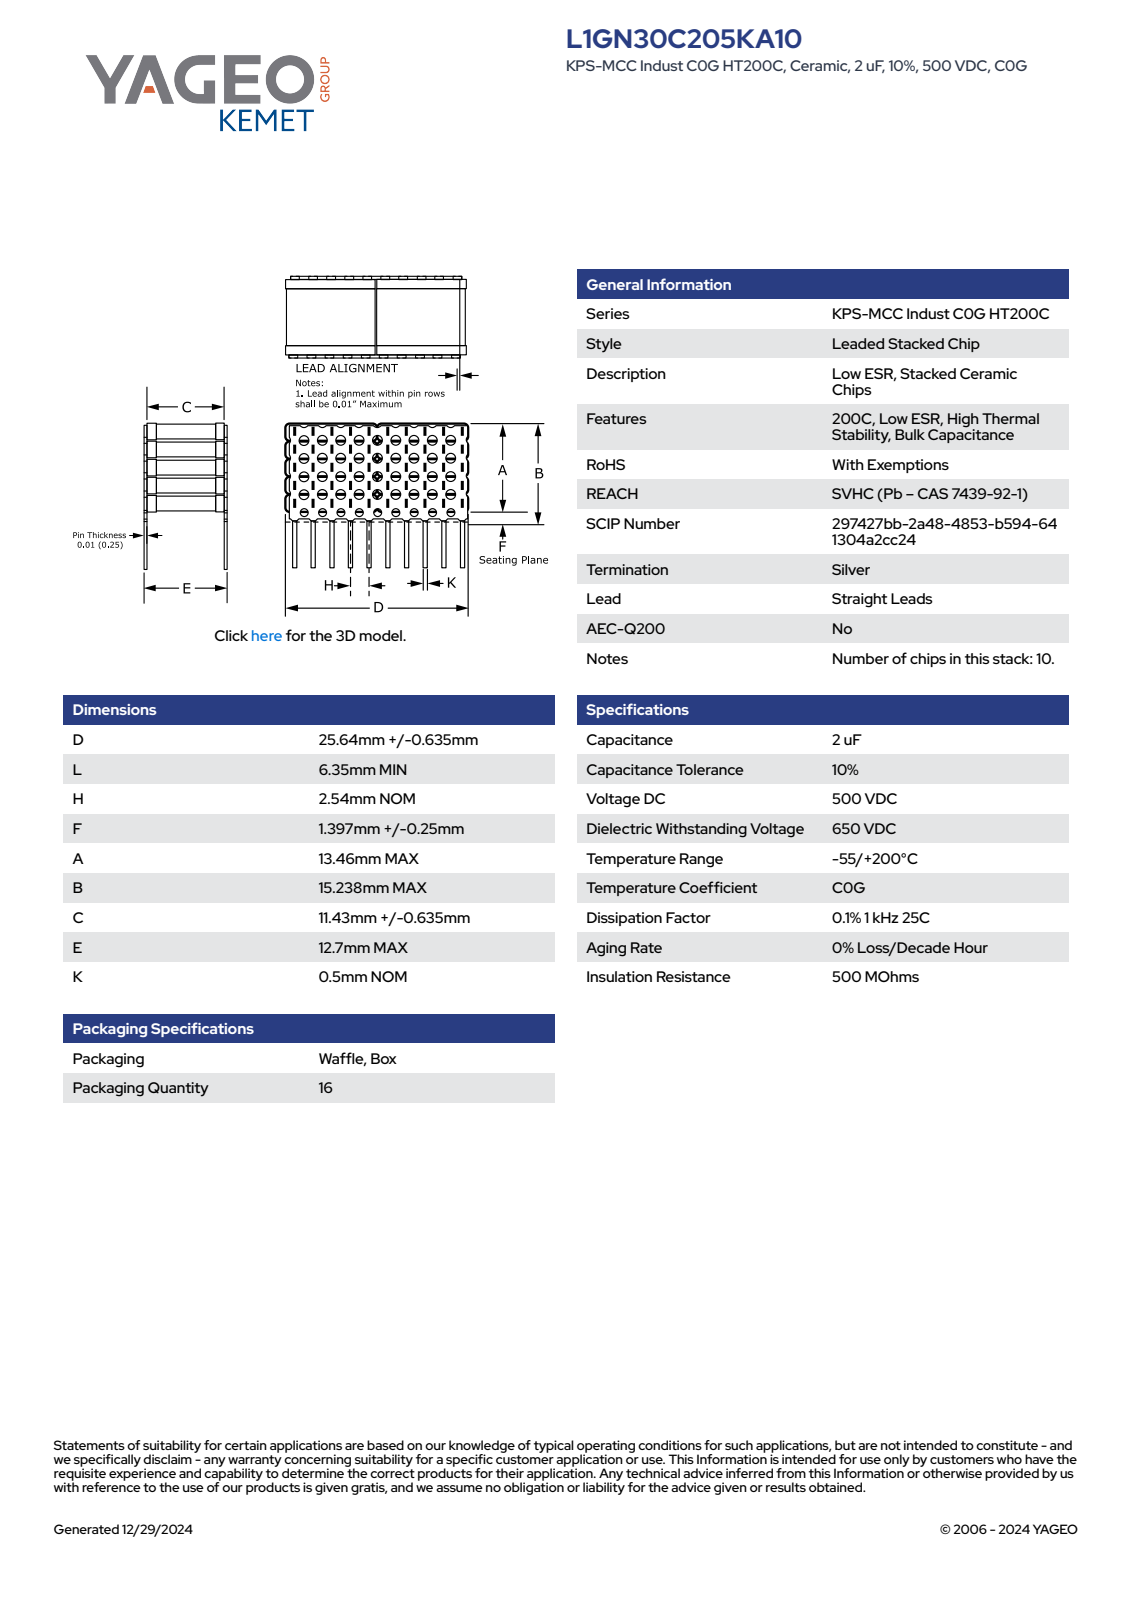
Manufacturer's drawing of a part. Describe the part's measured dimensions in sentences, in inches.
The part is named "CCSS_LSN3_3_D26.28L6.35H2.54F1.647A13.46B15.238C12.065E12.7K0.5". Its 3-D file was written by "SolidWorks 2014 (AUTOMOTIVE_DESIGN)". It is 1 solid with 402 faces: 402 planar, 0 cylindrical and 0 other. Overall it measures 1.035 by 0.85 by 0.497 inches. Its volume is 0.258 cubic inches and its surface area 7.617 square inches. The main face-to-face distances are 0.106, 0.212, 0.318, 0.212, 0.098, 0.108, 0.101, 0.103, 0.209, 0.207.
